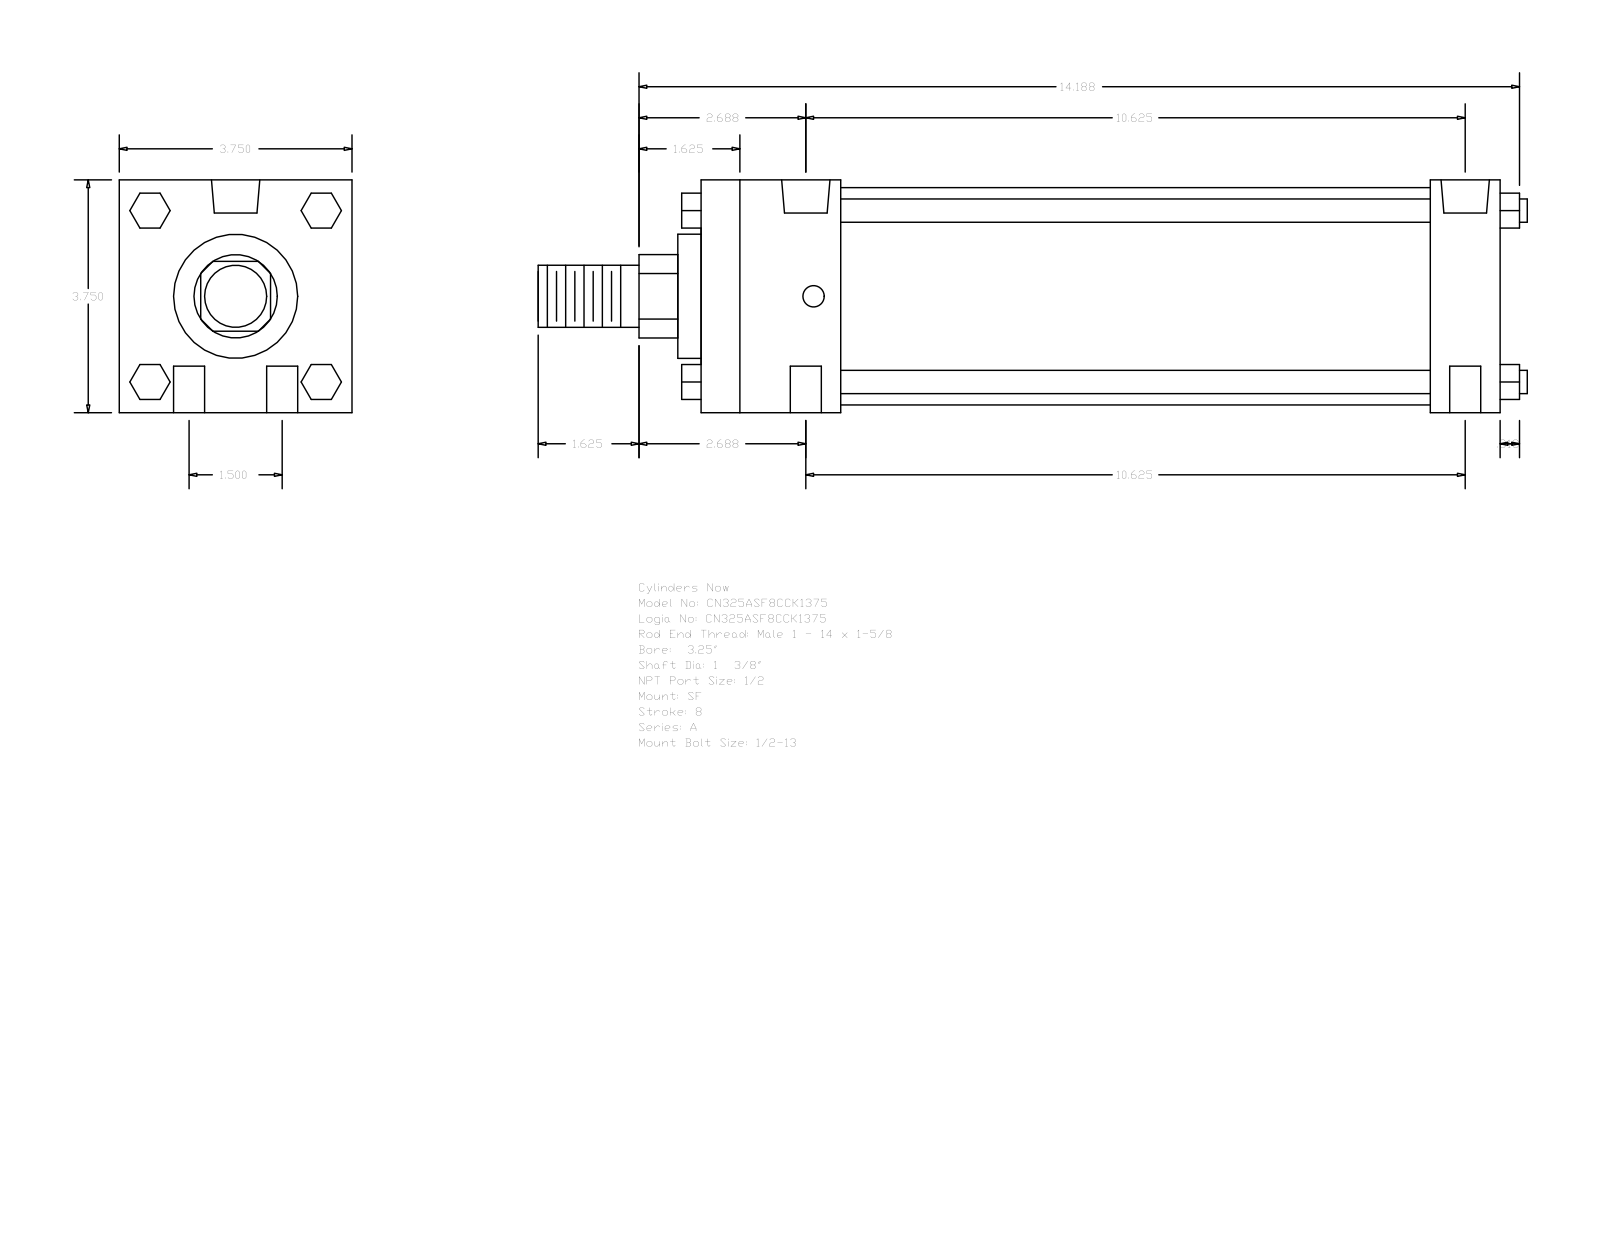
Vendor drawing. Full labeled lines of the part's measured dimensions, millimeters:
Part name (STEP PRODUCT): A_SF__0325_1.375
STEP written by: GSSL Pune (CONFIG_CONTROL_DESIGN)
Units: millimetres
Bodies: 0 solids, 124 faces (94 planar, 30 cylindrical, 0 other)
Overall size (bounding box): 404.81 × 95.25 × 95.25
Round holes (diameter × count): ⌀12.7 ×4, ⌀8.73 ×2, ⌀19.77 ×2
Round bosses / shafts (diameter × count): ⌀9.53 ×4, ⌀88.9 ×1, ⌀50.8 ×1, ⌀34.92 ×1, ⌀25.4 ×1
Partial cylindrical surfaces — rounded edges, fillets, slot ends (radius × count): R17.06 ×1
Main face-to-face distances: 95.24, 327.03, 57.15, 28.58, 298.45, 241.3, 269.88, 66.67, 9.52, 307.97
Hole centre spacings: 19.05, 270.55, 269.88, 38.1, 272.56, 263.52
